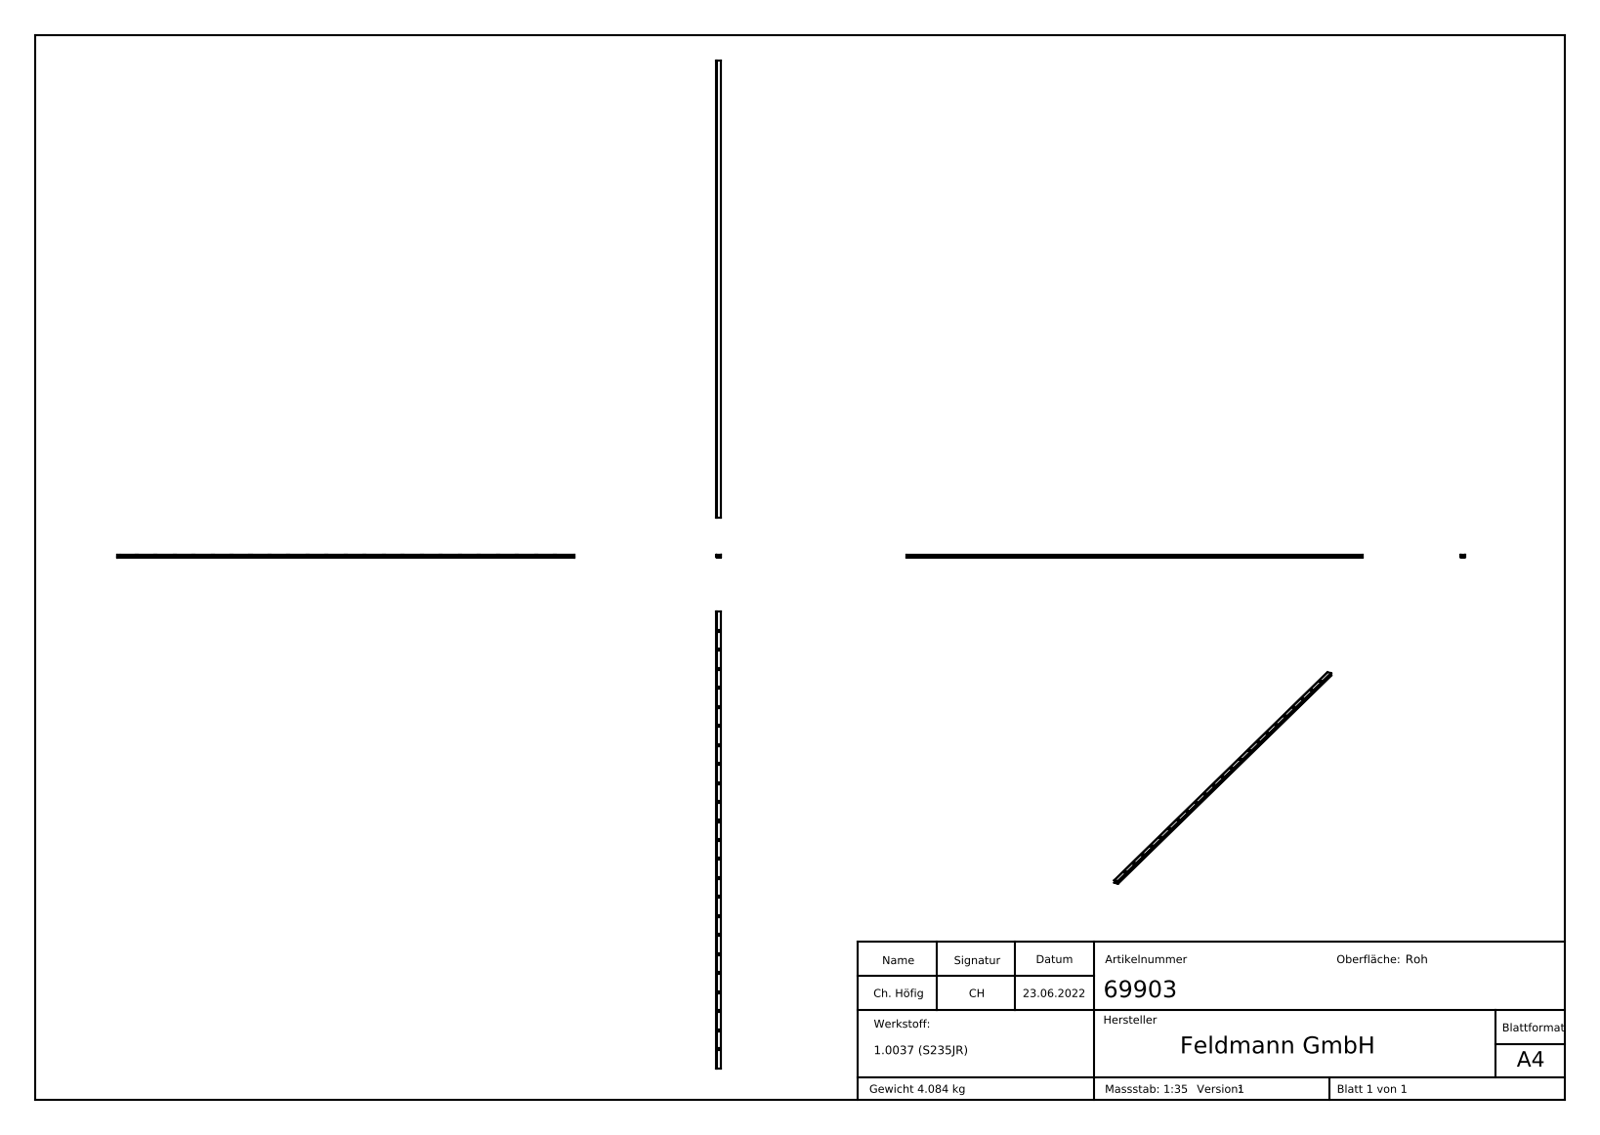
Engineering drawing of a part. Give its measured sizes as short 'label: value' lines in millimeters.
name: 69903
written by: SolidWorks 2018 (CONFIG_CONTROL_DESIGN)
unit: mm
bodies: 1 solid, 337 faces (211 planar, 8 cylindrical, 118 other)
size: 3000 × 30 × 20
volume: 523 623 mm³; area: 526 381 mm²
rounds: 4× R1, 4× R3
face distances: 2, 18, 28, 16, 20, 30, 26, 8.5, 21.5, 6.5
